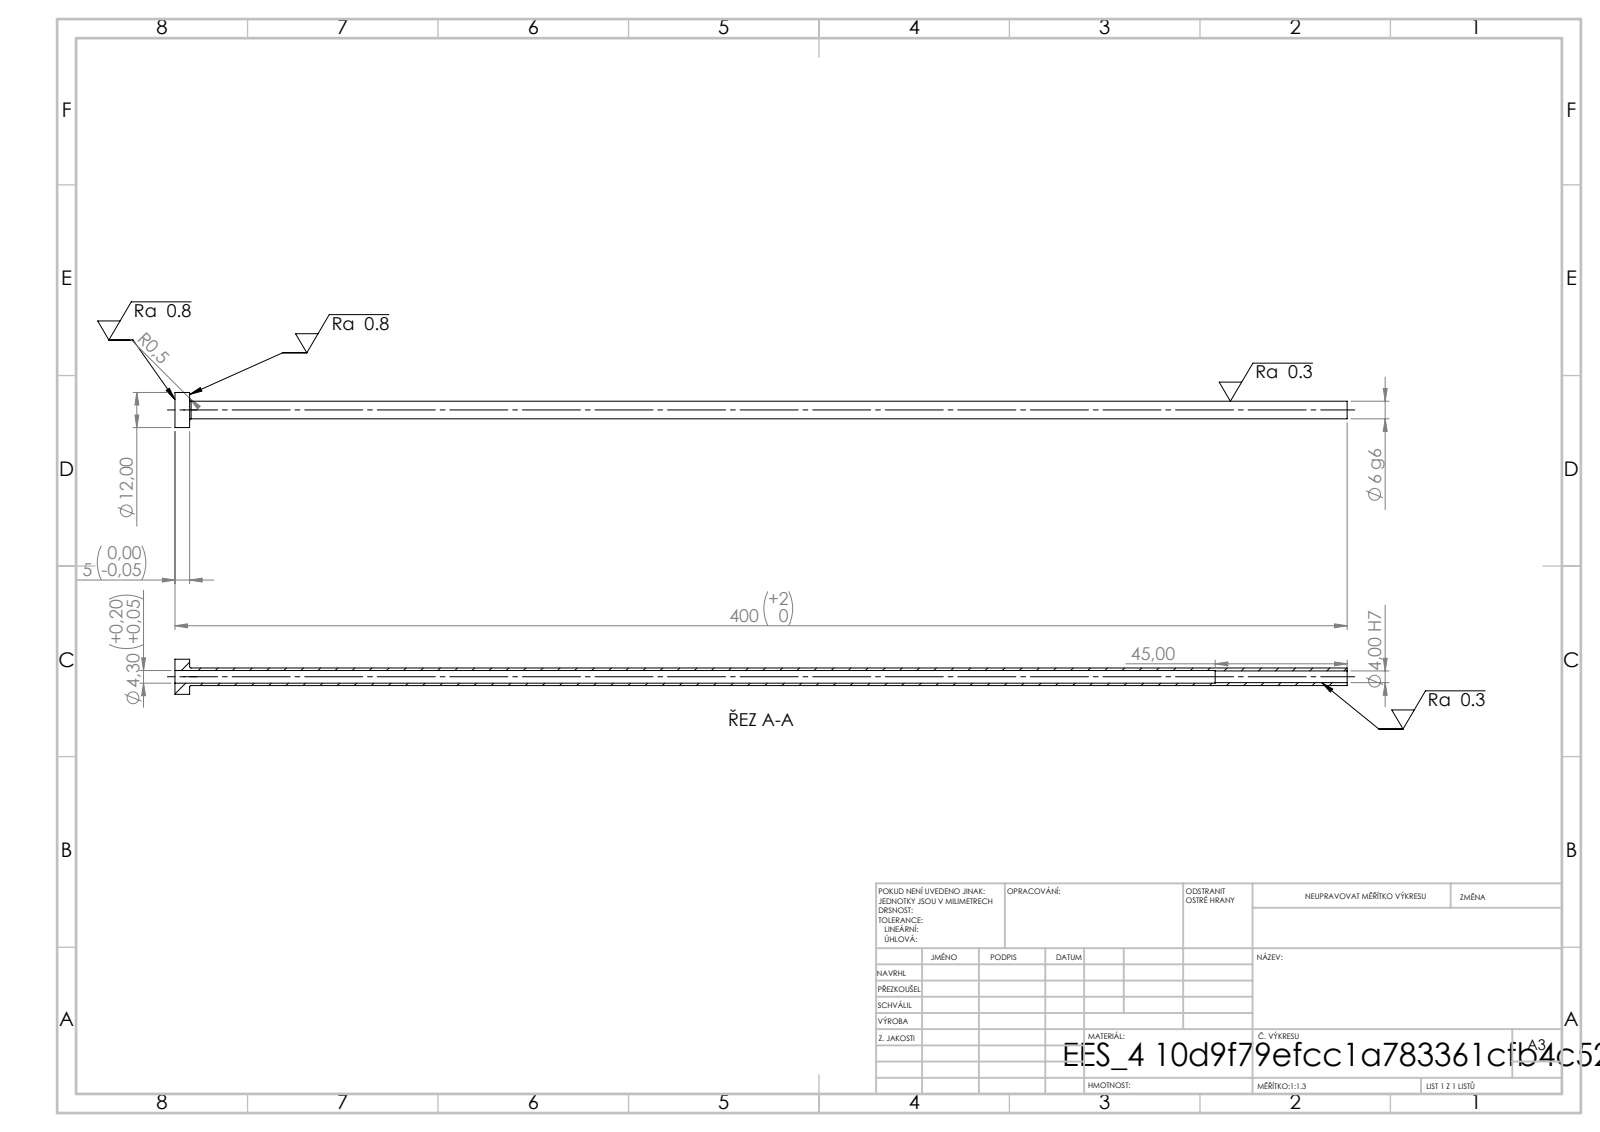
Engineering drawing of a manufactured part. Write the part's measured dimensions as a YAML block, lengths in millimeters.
step_written_by: "SolidWorks 2019 (CONFIG_CONTROL_DESIGN)"
units: millimeters
bodies: {solids: 1, faces: 14, planar: 4, cylindrical: 8, other: 2}
overall_size: [400, 12, 12]
volume: 6014
surface_area: 13192
round_holes:
  - {diameter: 4, count: 1}
  - {diameter: 4.3, count: 1}
round_bosses_or_shafts:
  - {diameter: 12, count: 1}
  - {diameter: 6, count: 1}
face_to_face_distances: [5, 400, 395, 355, 350, 45]
